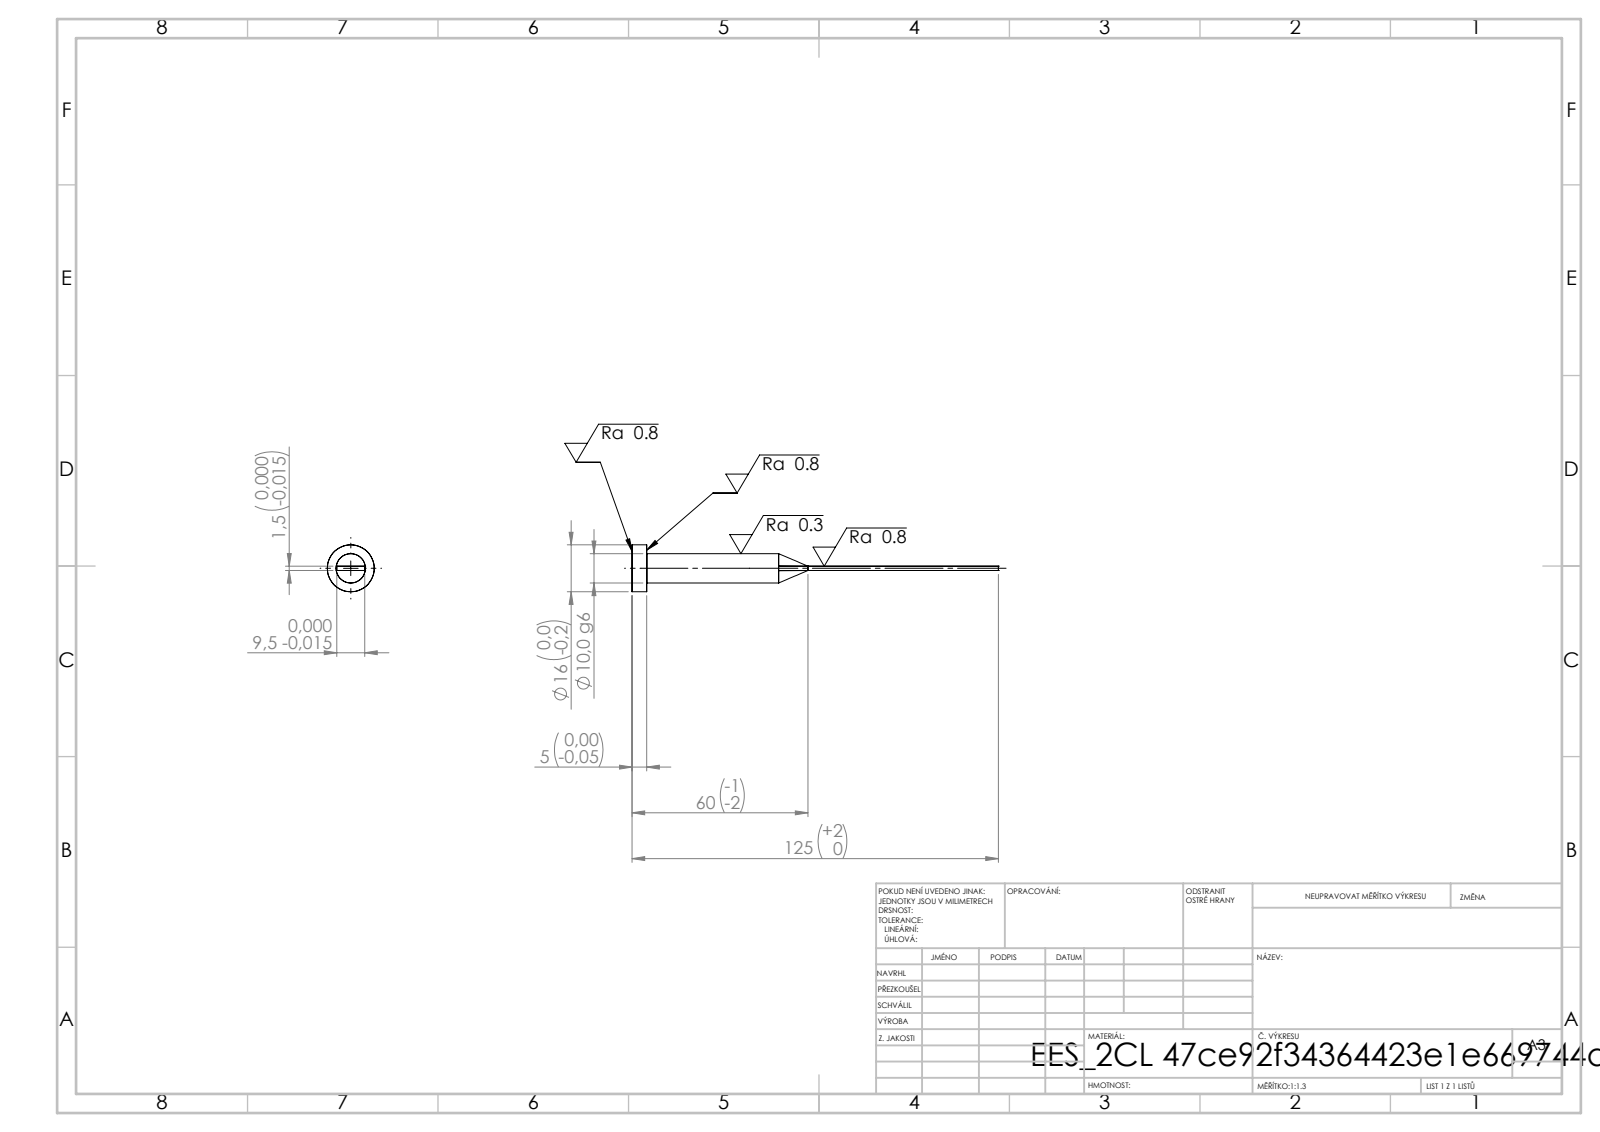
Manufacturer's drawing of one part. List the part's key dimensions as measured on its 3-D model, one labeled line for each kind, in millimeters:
STEP written by: SolidWorks 2019 (CONFIG_CONTROL_DESIGN)
Units: millimetres
Bodies: 1 solid, 15 faces (7 planar, 4 cylindrical, 4 other)
Overall size (bounding box): 125 × 16 × 16
Volume: 5 904 mm³ · Surface area: 3 697 mm²
Round bosses / shafts (diameter × count): ⌀16 ×1, ⌀10 ×1
Main face-to-face distances: 1.5, 5, 9.5, 125, 120
